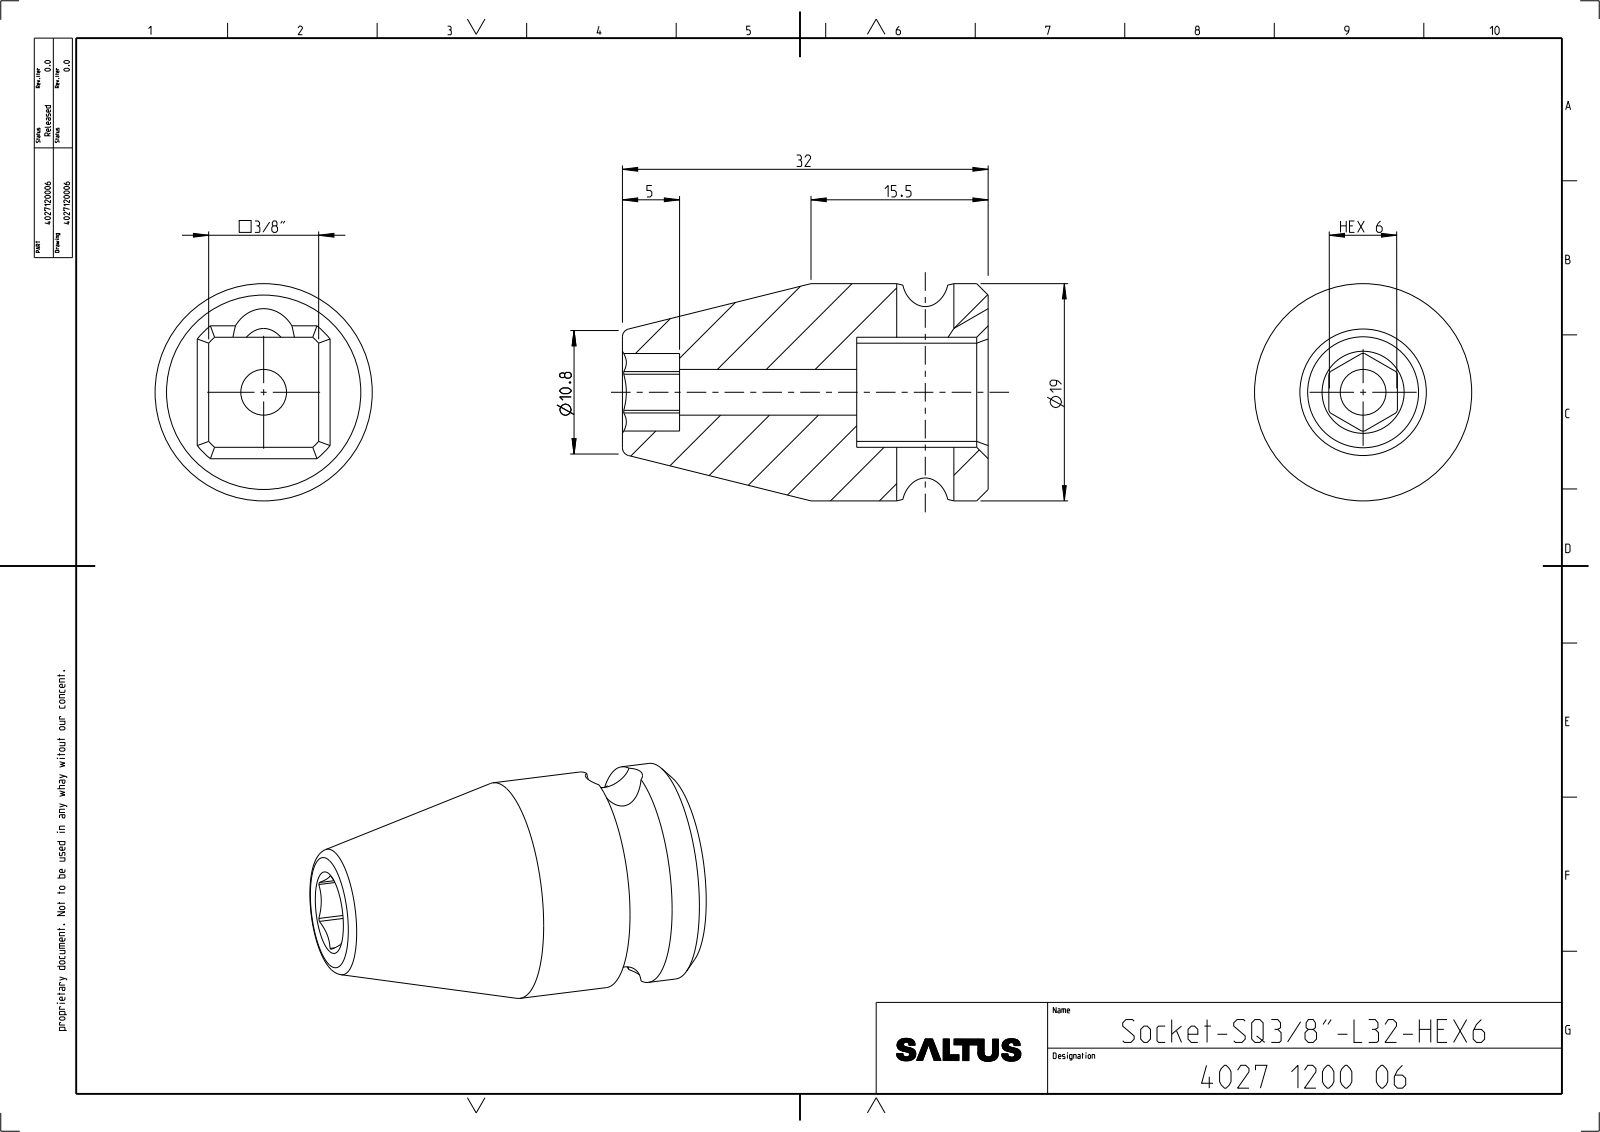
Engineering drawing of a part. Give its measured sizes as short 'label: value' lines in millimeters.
name: 4027120006
written by: CREO PARAMETRIC BY PTC INC, 2022414 (CONFIG_CONTROL_DESIGN)
unit: mm
bodies: 1 solid, 54 faces (19 planar, 21 cylindrical, 14 other)
size: 32 × 19 × 19
volume: 5 470 mm³; area: 2 815 mm²
holes: 1× ⌀4, 1× ⌀5
bosses: 1× ⌀19
rounds: 1× R3, 1× R3.39, 1× R6.45
face distances: 9.62, 11.5, 6, 32, 20.5, 1.81, 7.81, 27, 15.5, 5
